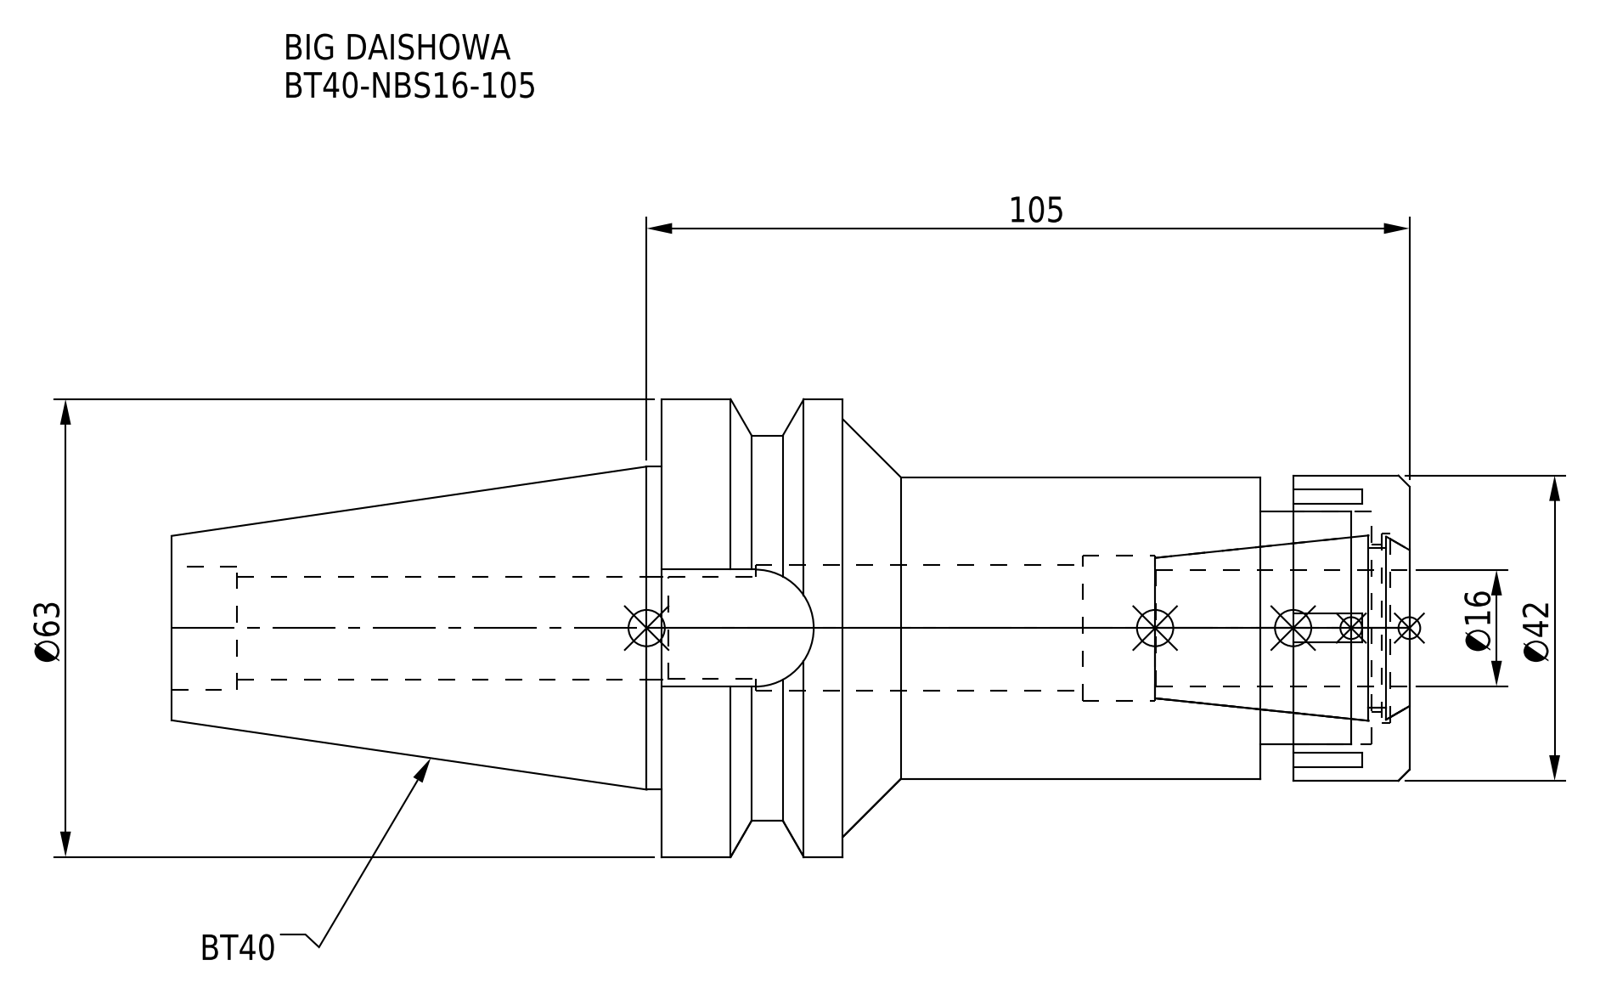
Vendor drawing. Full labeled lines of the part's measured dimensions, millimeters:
Part name (STEP PRODUCT): BT40-NBS16-105.stp; BT40-NBS16-105; NBN16_1.stp; BT40-NBS16-105-FreeParts (+3 more)
STEP written by: SolidWorks 2019 (CONFIG_CONTROL_DESIGN)
Units: millimetres
Bodies: 2 solids, 93 faces (45 planar, 34 cylindrical, 14 other)
Overall size (bounding box): 170.4 × 63 × 63
Volume: 199 815 mm³ · Surface area: 41 042 mm²
Round holes (diameter × count): ⌀14 ×1, ⌀14.2 ×1, ⌀17 ×1, ⌀17.3 ×1, ⌀20 ×1, ⌀23 ×1, ⌀26 ×1, ⌀32 ×1
Round bosses / shafts (diameter × count): ⌀63 ×1, ⌀53 ×1, ⌀44.45 ×1, ⌀42 ×1, ⌀41.5 ×1
Partial cylindrical surfaces — rounded edges, fillets, slot ends (radius × count): R8.05 ×1
Main face-to-face distances: 103, 8, 20.5, 82.5, 16, 4.5, 87, 78, 62, 57.5
